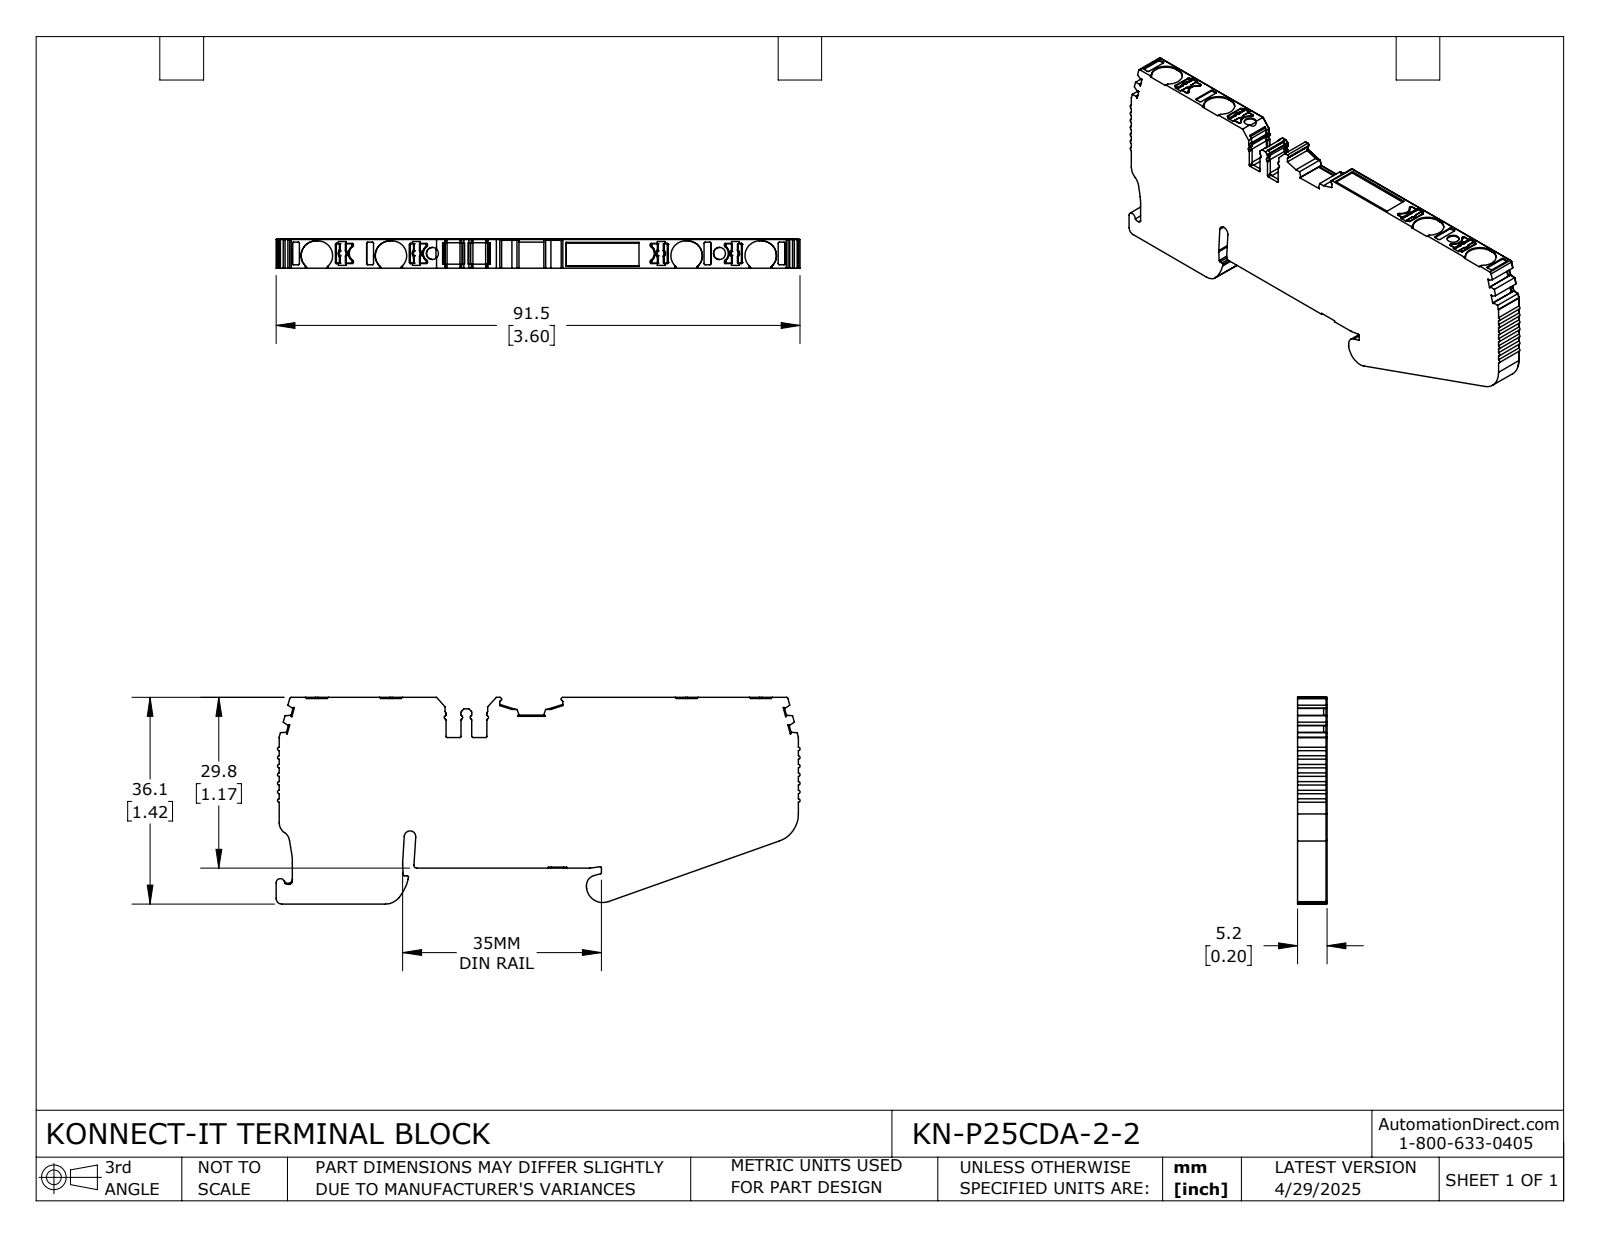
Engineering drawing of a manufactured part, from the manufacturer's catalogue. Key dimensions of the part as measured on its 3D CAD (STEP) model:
Part name (STEP PRODUCT): KN-P25CDA-2-2
STEP written by: SolidWorks 2024 (CONFIG_CONTROL_DESIGN)
Units: inches
Bodies: 1 solid, 748 faces (386 planar, 291 cylindrical, 71 other)
Overall size (bounding box): 3.602 × 1.42 × 0.203
Volume: 0.855 in³ · Surface area: 11.07 in²
Round holes (diameter × count): ⌀0.083 ×2
Partial cylindrical surfaces — rounded edges, fillets, slot ends (radius × count): R0.008 ×78, R0.012 ×39, R0.004 ×21, R0.02 ×18, R0.006 ×16, R0.016 ×9, R0.1 ×8, R0.059 ×4
Main face-to-face distances: 0.203, 1.166, 1.174, 0.246, 1.412, 1.42, 3.569, 0.197, 0.177, 0.047
Hole centre spacings: 1.973
